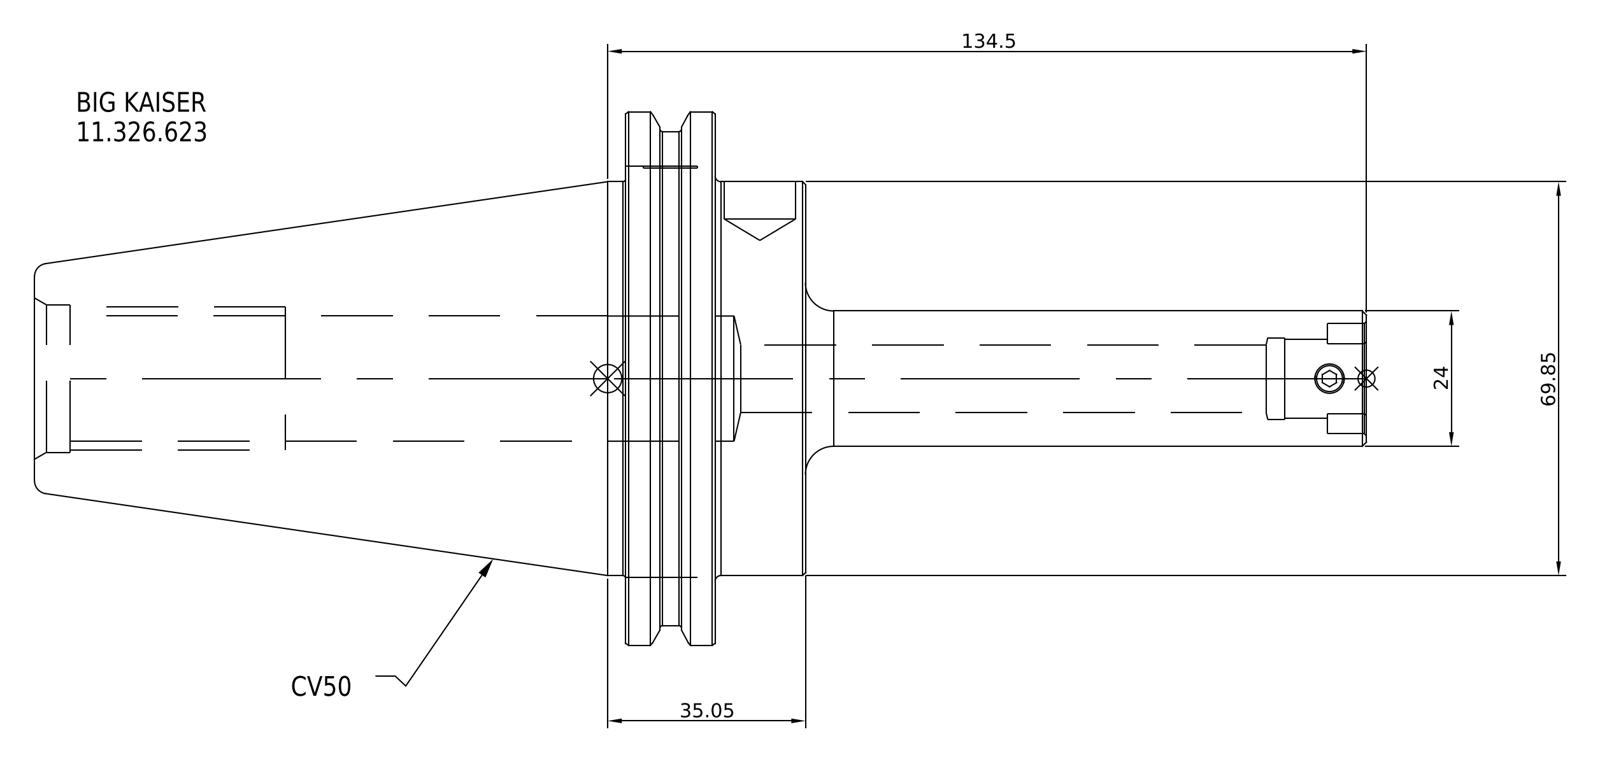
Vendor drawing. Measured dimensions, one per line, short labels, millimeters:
name: 11.326.623
written by: SolidWorks 2021 (CONFIG_CONTROL_DESIGN)
unit: mm
bodies: 1 solid, 16 faces (7 planar, 6 cylindrical, 3 other)
size: 236.1 × 98.43 × 98.43
volume: 487 493 mm³; area: 48 475 mm²
bosses: 1× ⌀98.43, 1× ⌀91.29, 1× ⌀69.85, 1× ⌀24
face distances: 17.55, 15.95, 33.5, 136.6, 120.65, 103.1, 99.5, 115.45, 133, 236.1
